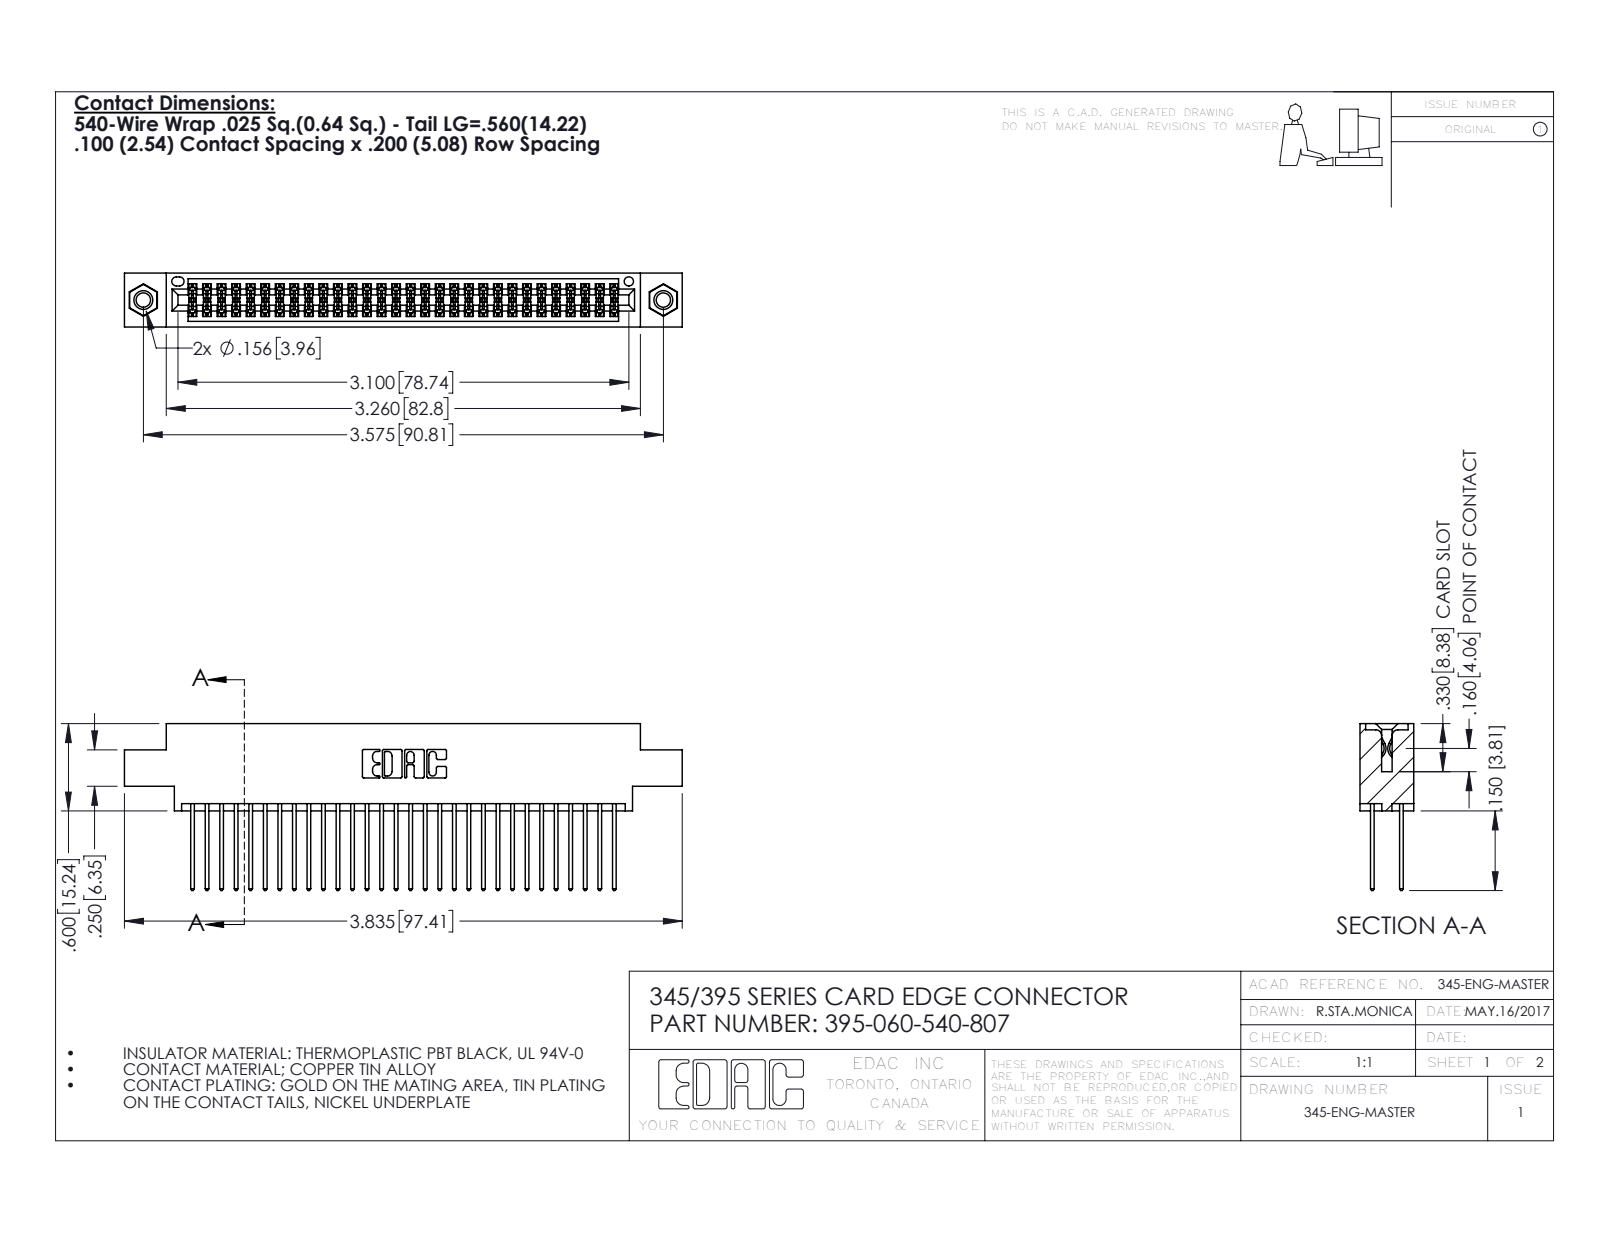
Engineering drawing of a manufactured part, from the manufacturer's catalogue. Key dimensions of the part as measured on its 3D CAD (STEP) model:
Part name (STEP PRODUCT): 345-250-001_345-250-005-103; 395-060-540-807; 345 Part_0.170 Offset - 0.156 Dia-TI; 345-292-001_345-293-140
STEP written by: SolidWorks 2016 (CONFIG_CONTROL_DESIGN)
Units: inches
Bodies: 63 solids, 3190 faces (2096 planar, 1078 cylindrical, 16 other)
Overall size (bounding box): 3.835 × 1.147 × 0.37
Volume: 0.577 in³ · Surface area: 23.2 in²
Round holes (diameter × count): ⌀0.098 ×2, ⌀0.125 ×2, ⌀0.156 ×2, ⌀0.064 ×1
Round bosses / shafts (diameter × count): ⌀0.155 ×2
Partial cylindrical surfaces — rounded edges, fillets, slot ends (radius × count): R0.006 ×90, R0.01 ×60, R0.01 ×22, R0.007 ×6, R0.031 ×6, R0.026 ×3, R0.014 ×2, R0.019 ×2
Main face-to-face distances: 0.072, 0.298, 0.2, 0.098, 0.272, 0.025, 0.37, 0.225, 0.175, 0.149
Hole centre spacings: 0.27, 3.34, 3.575
